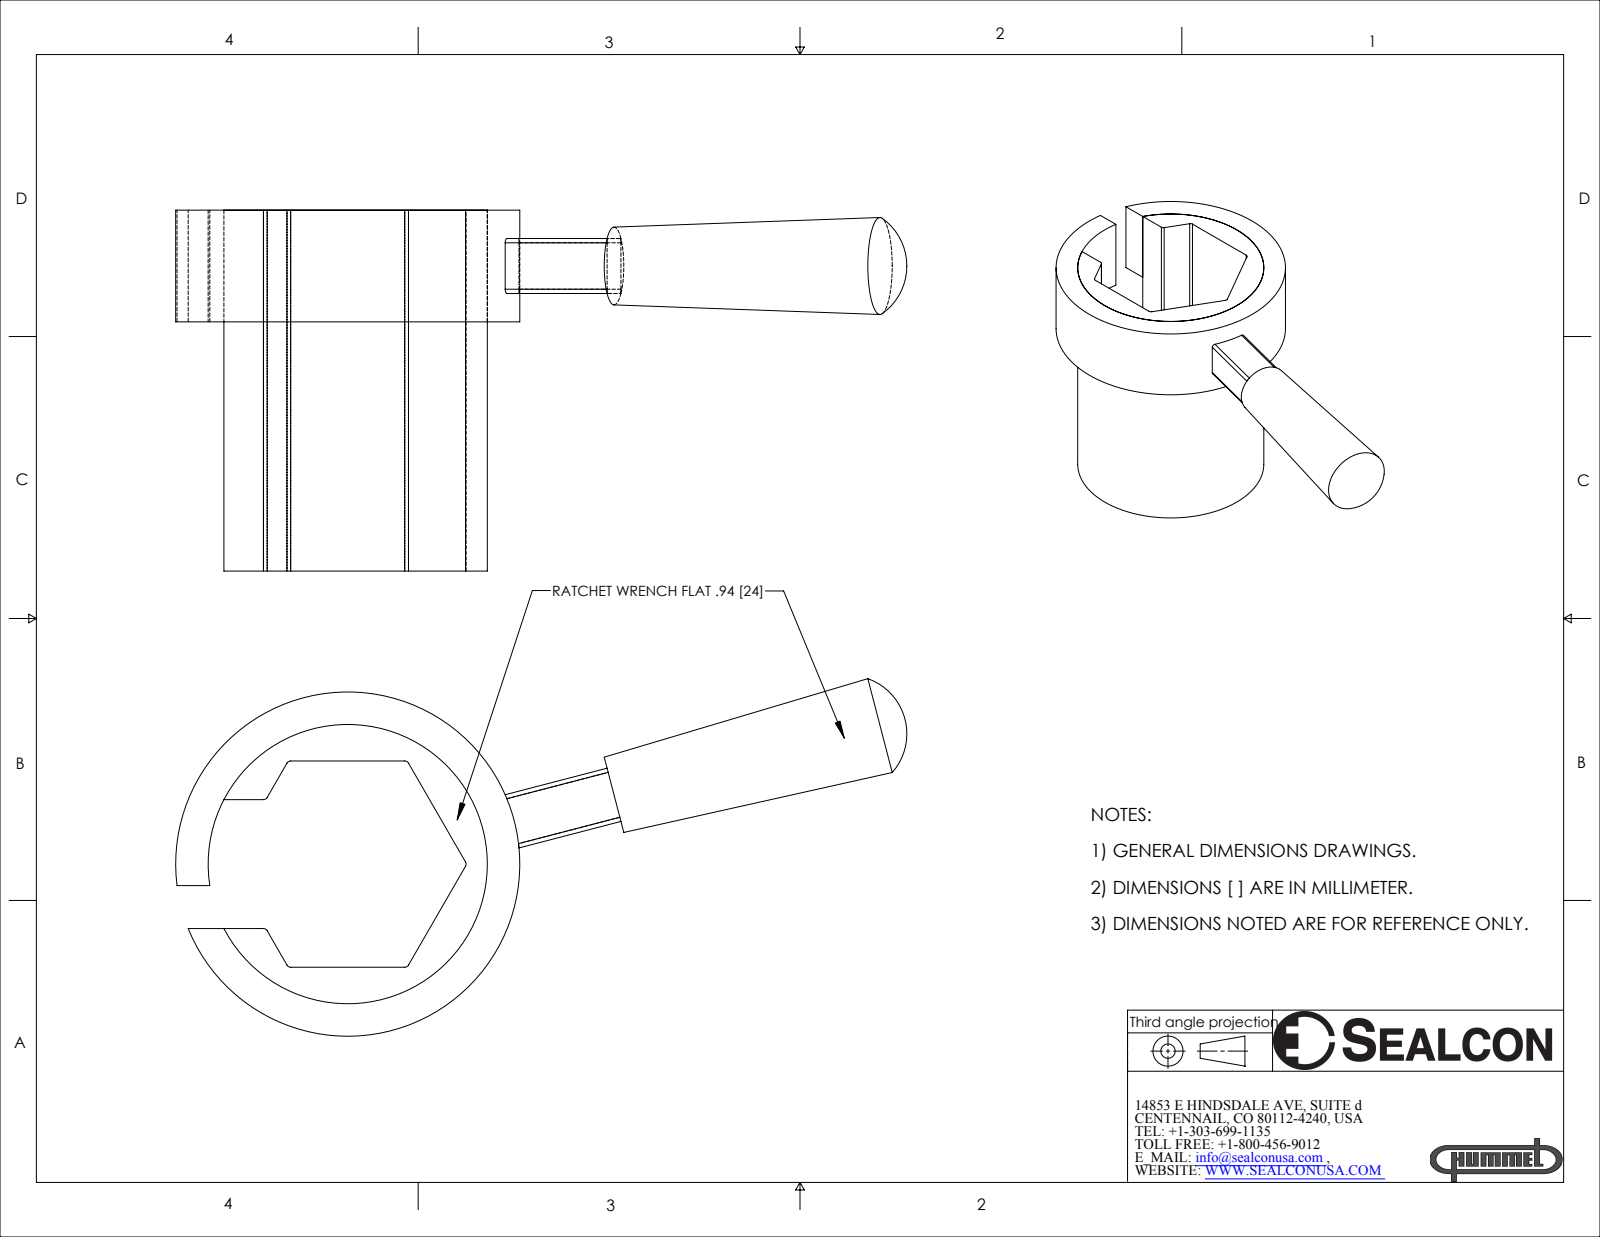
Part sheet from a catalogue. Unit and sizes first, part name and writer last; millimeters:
Units: millimetres
Overall size (bounding box): 85.12 × 42 × 41.61
Round holes (diameter × count): ⌀32.5 ×1
Round bosses / shafts (diameter × count): ⌀40.06 ×1
Partial cylindrical surfaces — rounded edges, fillets, slot ends (radius × count): R0.5 ×11
Main face-to-face distances: 24, 4.5, 19.5, 13, 29, 42, 15, 6.4, 3.3, 9.7
Volume: 20 007 mm³ · Surface area: 12 605 mm²
Bodies: 3 solids, 43 faces (19 planar, 20 cylindrical, 4 other)
Part name (STEP PRODUCT): R-2400-WR
STEP written by: SolidWorks 2007 (CONFIG_CONTROL_DESIGN)
